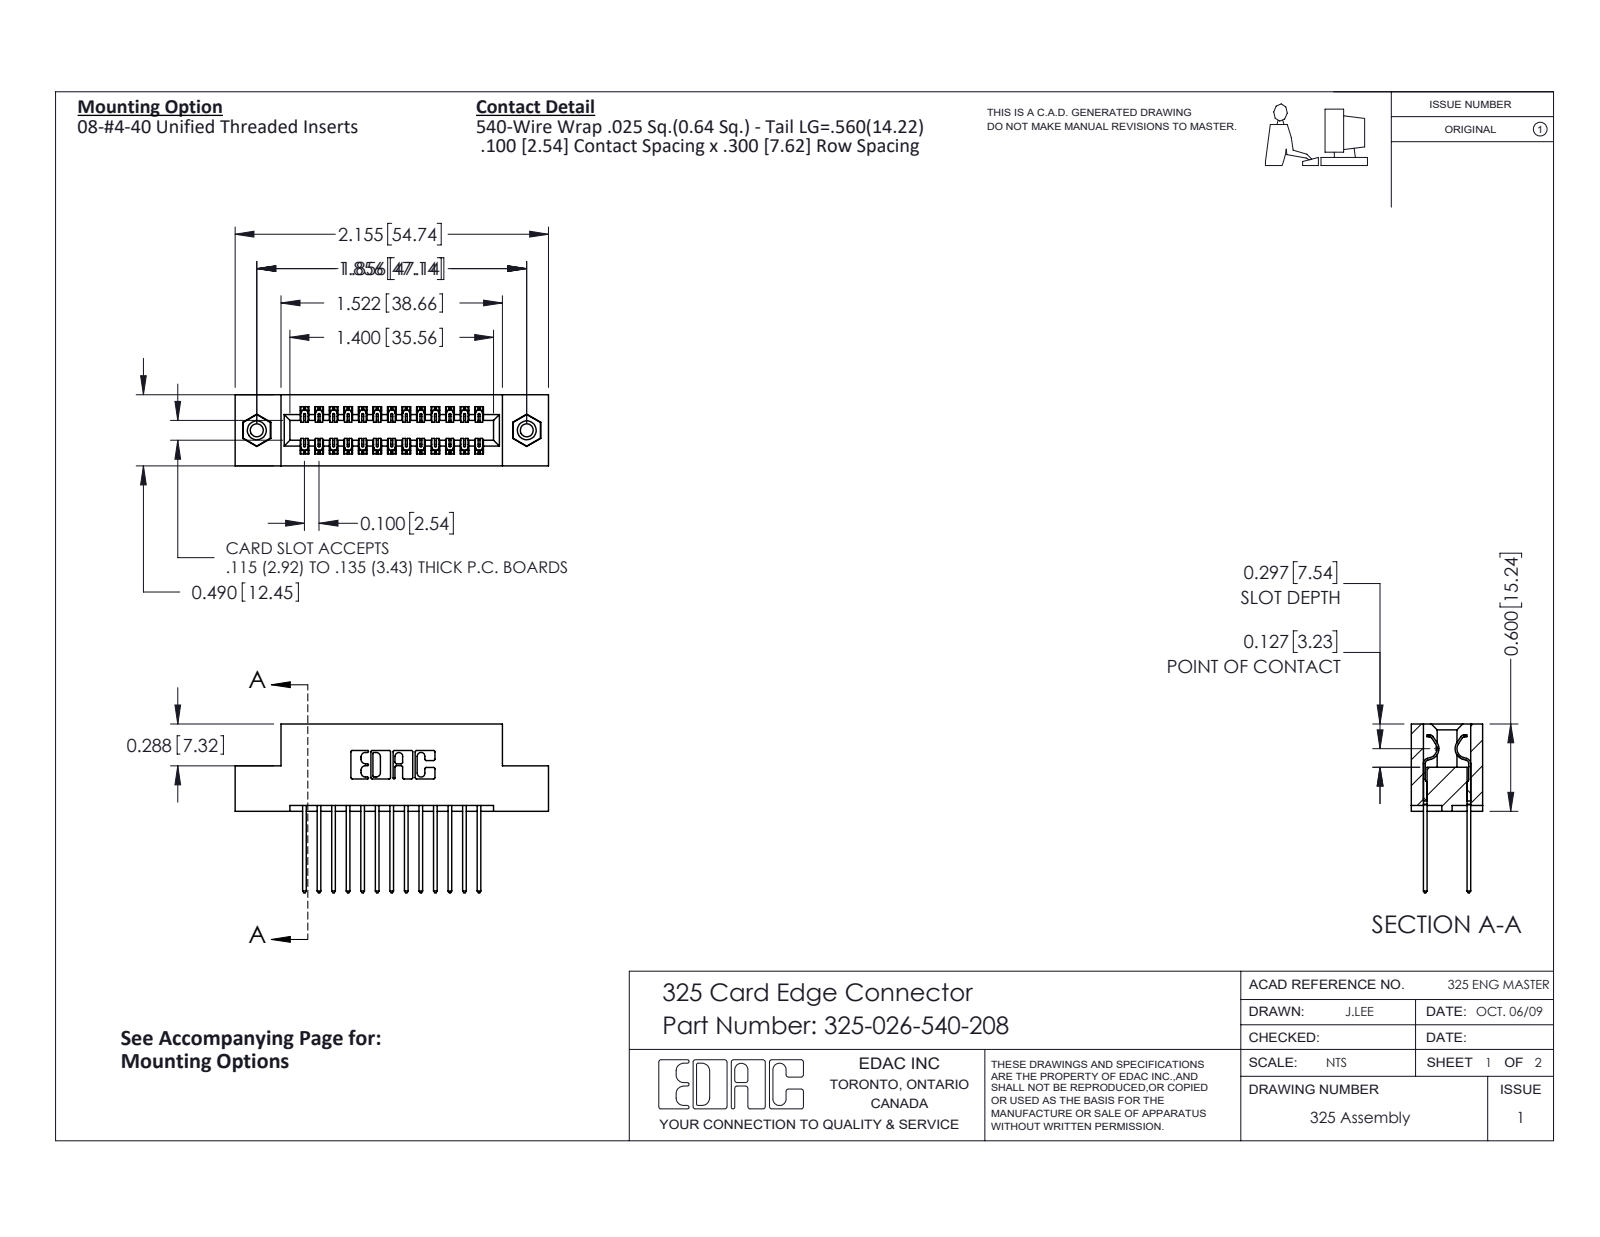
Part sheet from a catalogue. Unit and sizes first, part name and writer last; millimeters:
Units: millimetres
Overall size (bounding box): 54.7 × 29.5 × 12.4
Round holes (diameter × count): ⌀2.3 ×2, ⌀3.2 ×2, ⌀4.1 ×2
Round bosses / shafts (diameter × count): ⌀3.9 ×2
Partial cylindrical surfaces — rounded edges, fillets, slot ends (radius × count): R0.2 ×39, R0.3 ×26, R0.3 ×22, R0.2 ×6, R0.8 ×6, R0.7 ×3, R0.4 ×2, R0.6 ×2
Main face-to-face distances: 2.1, 10.3, 7.6, 12.4, 2.7, 9.7, 0.6, 8.3, 1, 2.5
Hole centre spacings: 47.1
Volume: 6 900 mm³ · Surface area: 8 142 mm²
Bodies: 29 solids, 1526 faces (1038 planar, 472 cylindrical, 16 other)
Part name (STEP PRODUCT): 325 Part_TI; 325-292-001_325-293-140; 345-250-001_345-250-003-102; 325-026-540-208
STEP written by: SolidWorks 2016 (CONFIG_CONTROL_DESIGN)
